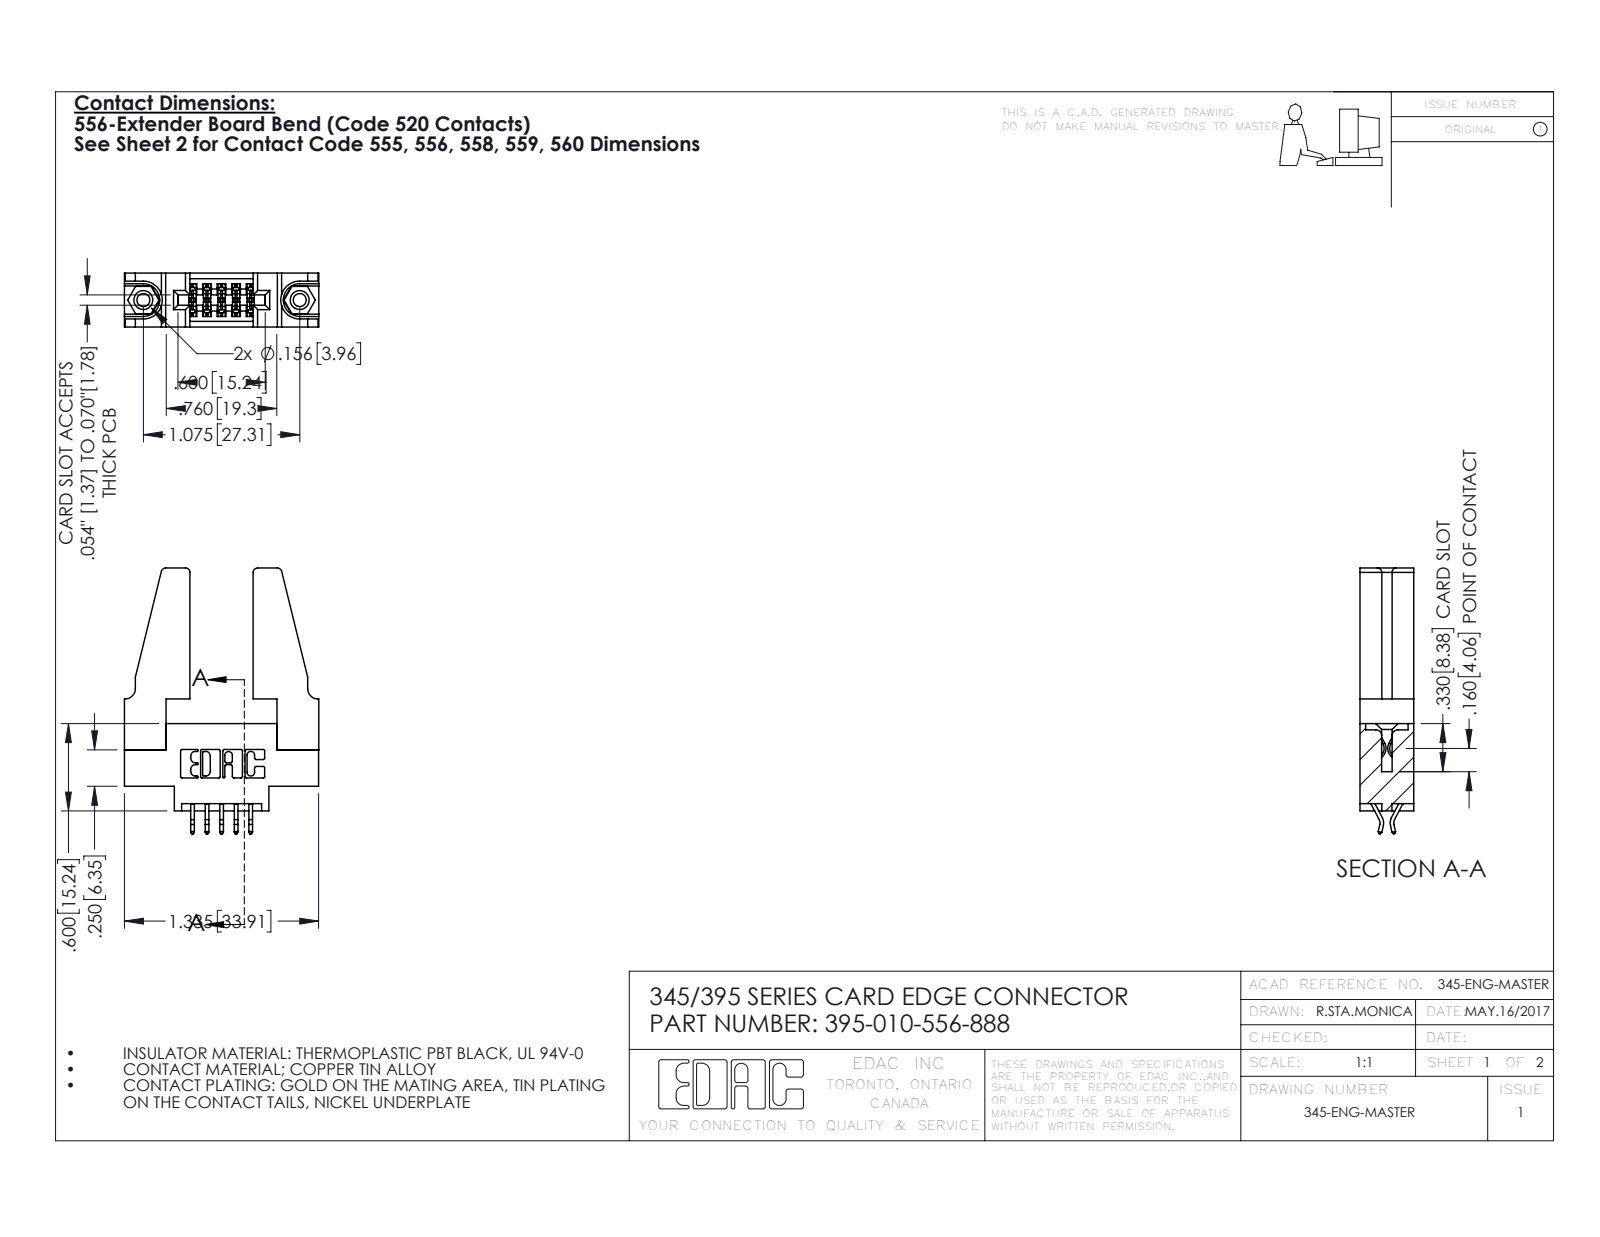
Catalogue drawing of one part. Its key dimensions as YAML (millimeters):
part_name: "345-250-001_345-250-001-102; 395-010-556-888; 345-220-078_345-220-088; 345 Part_0.170 Offset - 0.156 Dia-TH (+1 more)"
step_written_by: "SolidWorks 2016 (CONFIG_CONTROL_DESIGN)"
units: millimeters
bodies: {solids: 15, faces: 814, planar: 526, cylindrical: 272, other: 16}
overall_size: [46.4, 33.9, 9.4]
volume: 6100
surface_area: 6735
round_holes:
  - {diameter: 2.3, count: 2}
  - {diameter: 3.2, count: 2}
  - {diameter: 4, count: 2}
  - {diameter: 1.6, count: 1}
round_bosses_or_shafts:
  - {diameter: 3.9, count: 2}
partial_cylinders:
  - {radius: 0.3, count: 22}
  - {radius: 0.2, count: 15}
  - {radius: 0.8, count: 8}
  - {radius: 0.2, count: 6}
  - {radius: 0.8, count: 6}
  - {radius: 0.7, count: 3}
  - {radius: 0.3, count: 2}
  - {radius: 0.4, count: 2}
face_to_face_distances: [9.4, 1.8, 7.6, 5.1, 3.8, 3.8, 5.6, 2, 5.7, 0.6]
hole_center_spacings: [6.9, 21.5, 27.3]
